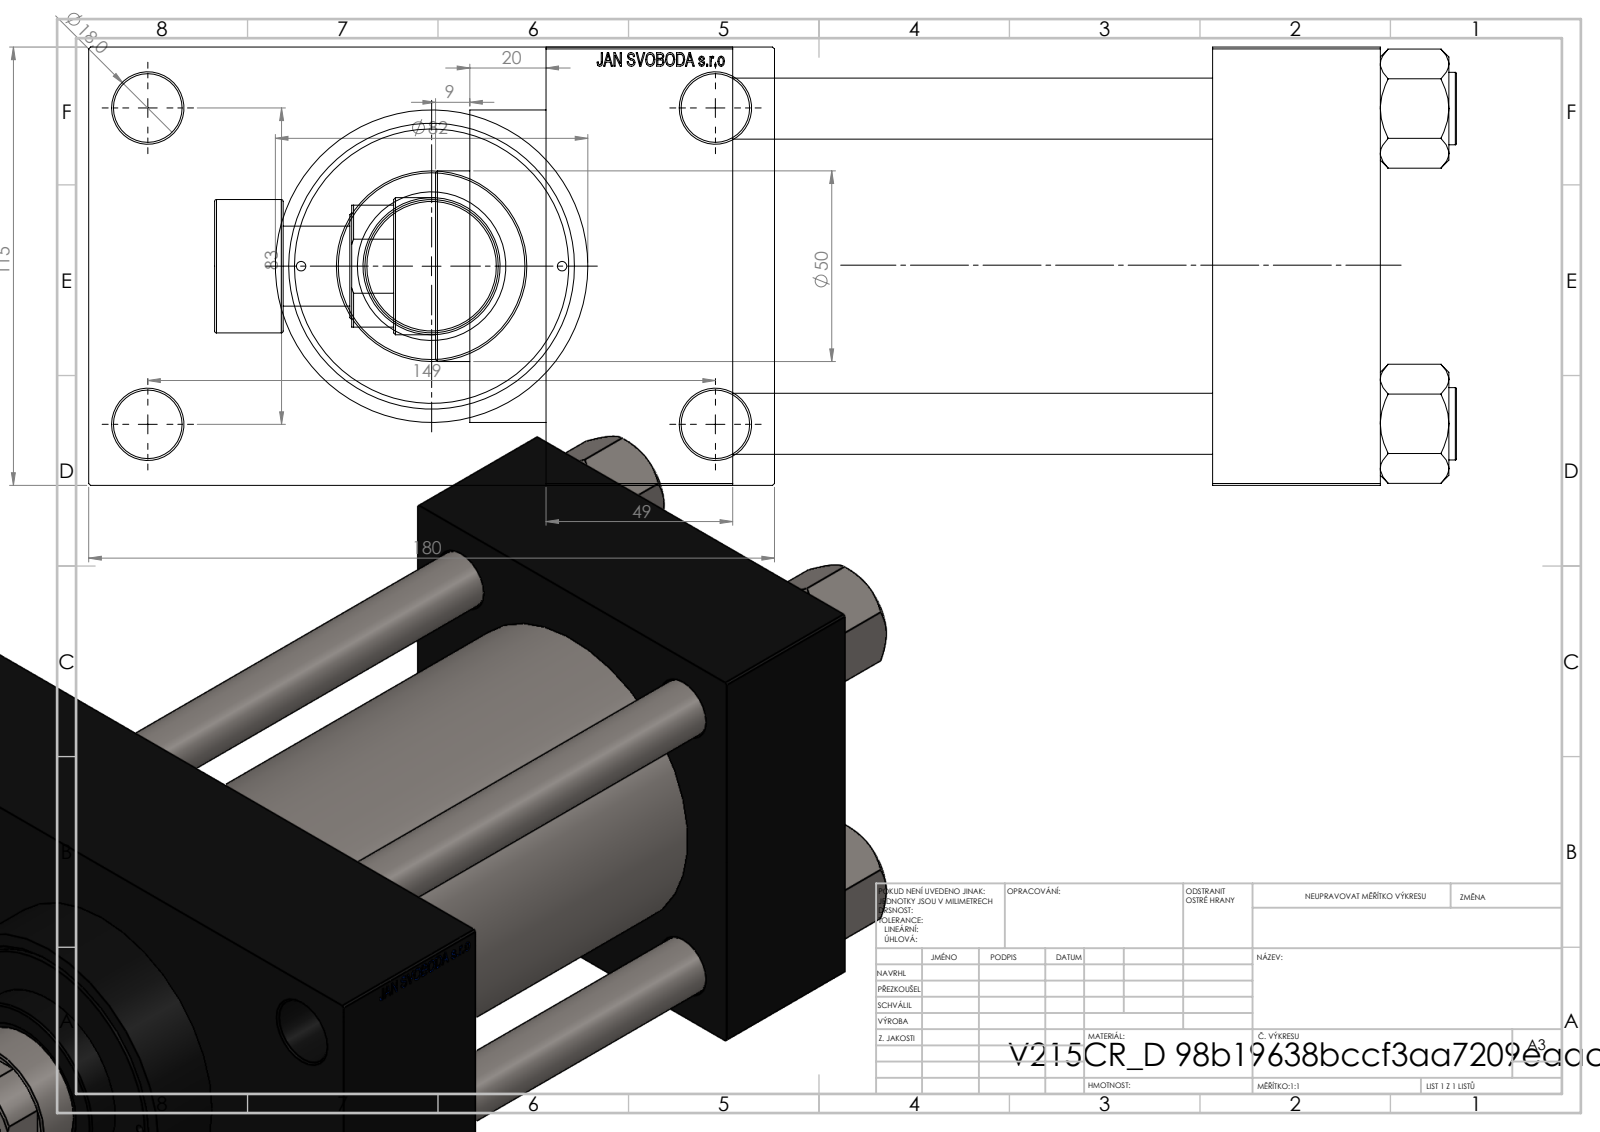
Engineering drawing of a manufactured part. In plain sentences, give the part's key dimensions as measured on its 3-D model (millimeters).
The part is named "NUT_M5_D; V215CR_D_TYCINKA; V215CR_ROD_END_F; V215_VC_A (+2 more)". Its 3-D file was written by "SolidWorks 2019 (CONFIG_CONTROL_DESIGN)". It is 12 solids with 1173 faces: 551 planar, 96 cylindrical and 526 other. Overall it measures 326 by 180 by 115 millimeters. Its volume is 2 159 000 cubic millimeters and its surface area 352 184 square millimeters. Round holes: 4 of diameter 16, 4 of diameter 18, 2 of diameter 2.5, 2 of diameter 7, 2 of diameter 26.44, 2 of diameter 35, 1 of diameter 25.5, 1 of diameter 36, 1 of diameter 39, 1 of diameter 61, 1 of diameter 72, 1 of diameter 80. Round bosses or shafts: 4 of diameter 19, 1 of diameter 86, 1 of diameter 82, 1 of diameter 50, 1 of diameter 35, 1 of diameter 21. The main face-to-face distances are 115, 126, 49, 175, 170, 44, 219, 32.5, 147.5, 180. The hole center spacings are 33.15, 41.96, 57.81, 58.48, 82.7, 85.28, 86.17, 89.24.
